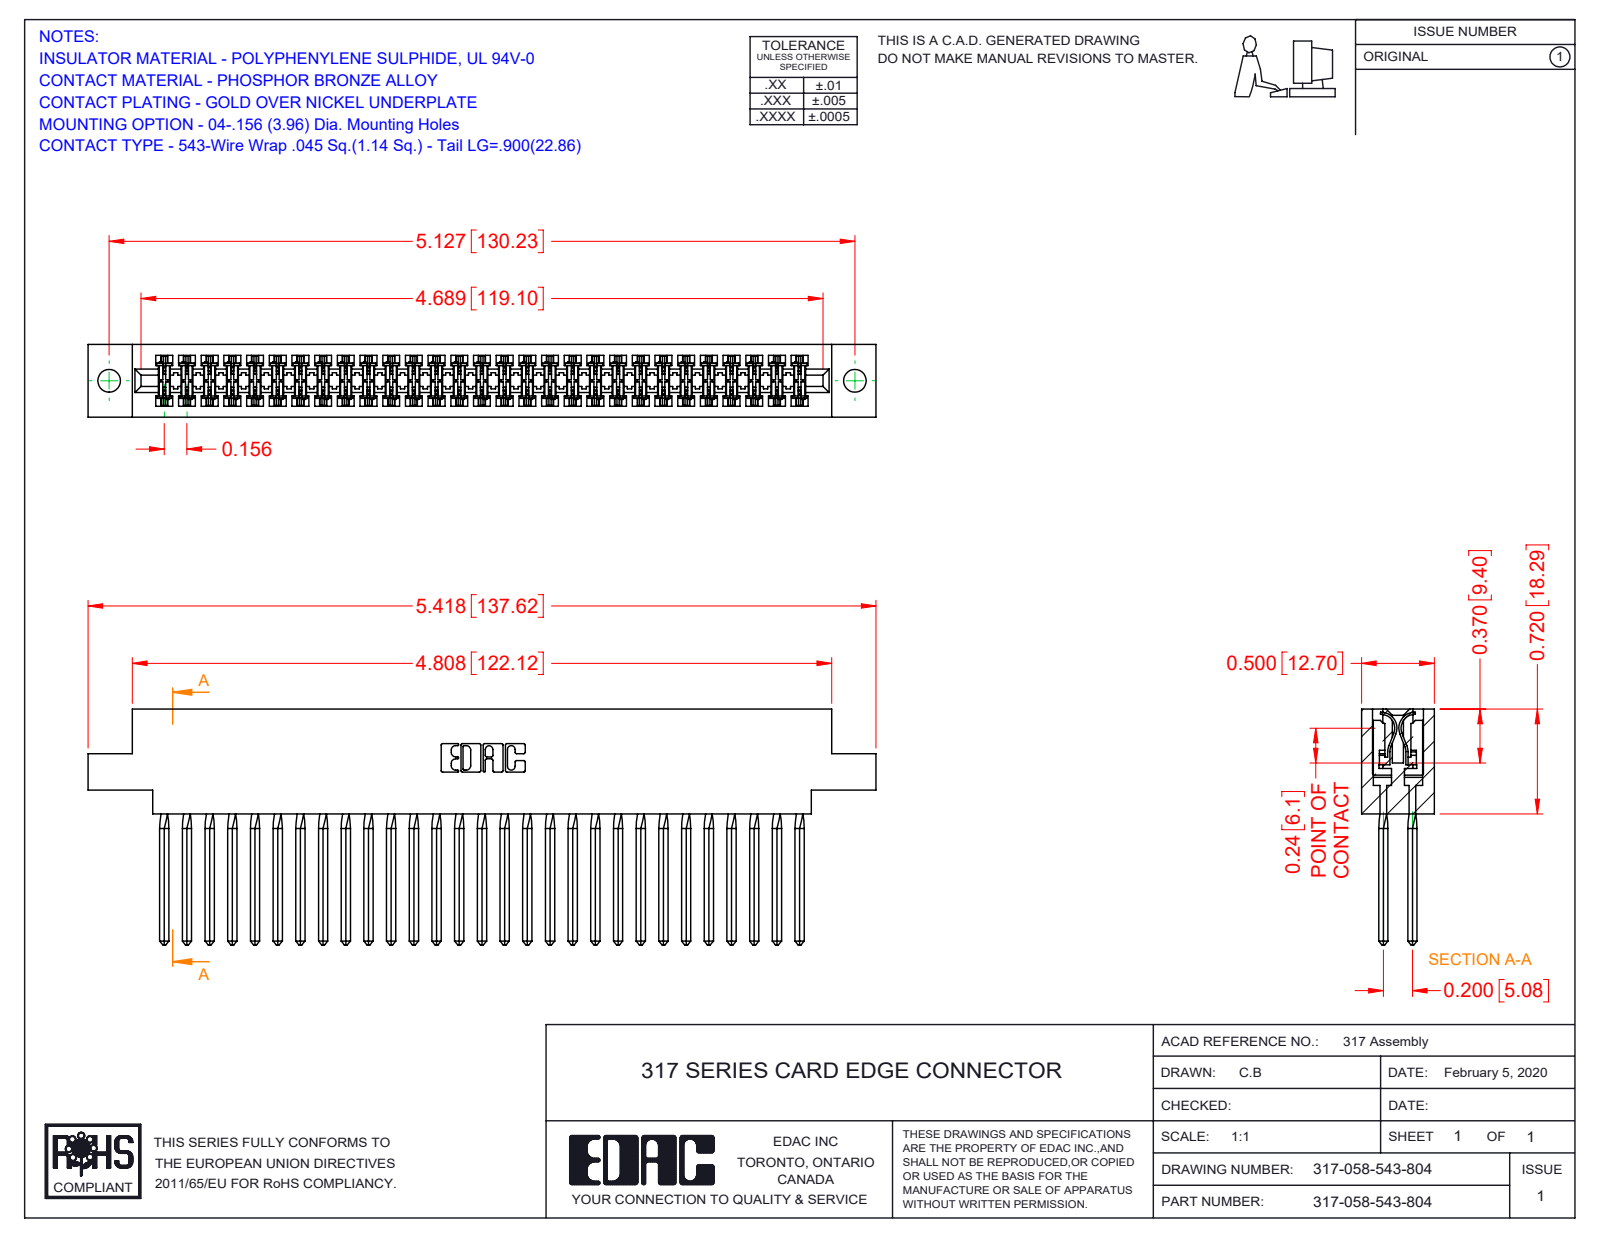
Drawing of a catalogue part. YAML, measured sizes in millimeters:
part_name: "317 Part_.156 Dia - TH; 317-058-543-804; 317-290-001_543"
step_written_by: "SolidWorks 2016 (CONFIG_CONTROL_DESIGN)"
units: millimeters
bodies: {solids: 59, faces: 5264, planar: 4292, cylindrical: 740, other: 232}
overall_size: [137.6, 41.1, 12.7]
volume: 22860
surface_area: 33990
round_holes:
  - {diameter: 4, count: 2}
partial_cylinders:
  - {radius: 0.4, count: 116}
  - {radius: 0.3, count: 22}
  - {radius: 0.2, count: 6}
  - {radius: 0.8, count: 6}
  - {radius: 0.7, count: 3}
  - {radius: 2.4, count: 2}
  - {radius: 2.5, count: 2}
  - {radius: 2.8, count: 2}
face_to_face_distances: [12.7, 1.9, 10.8, 8.9, 2.8, 5, 2.4, 5.1, 18.3, 2.9]
hole_center_spacings: [130.2]
